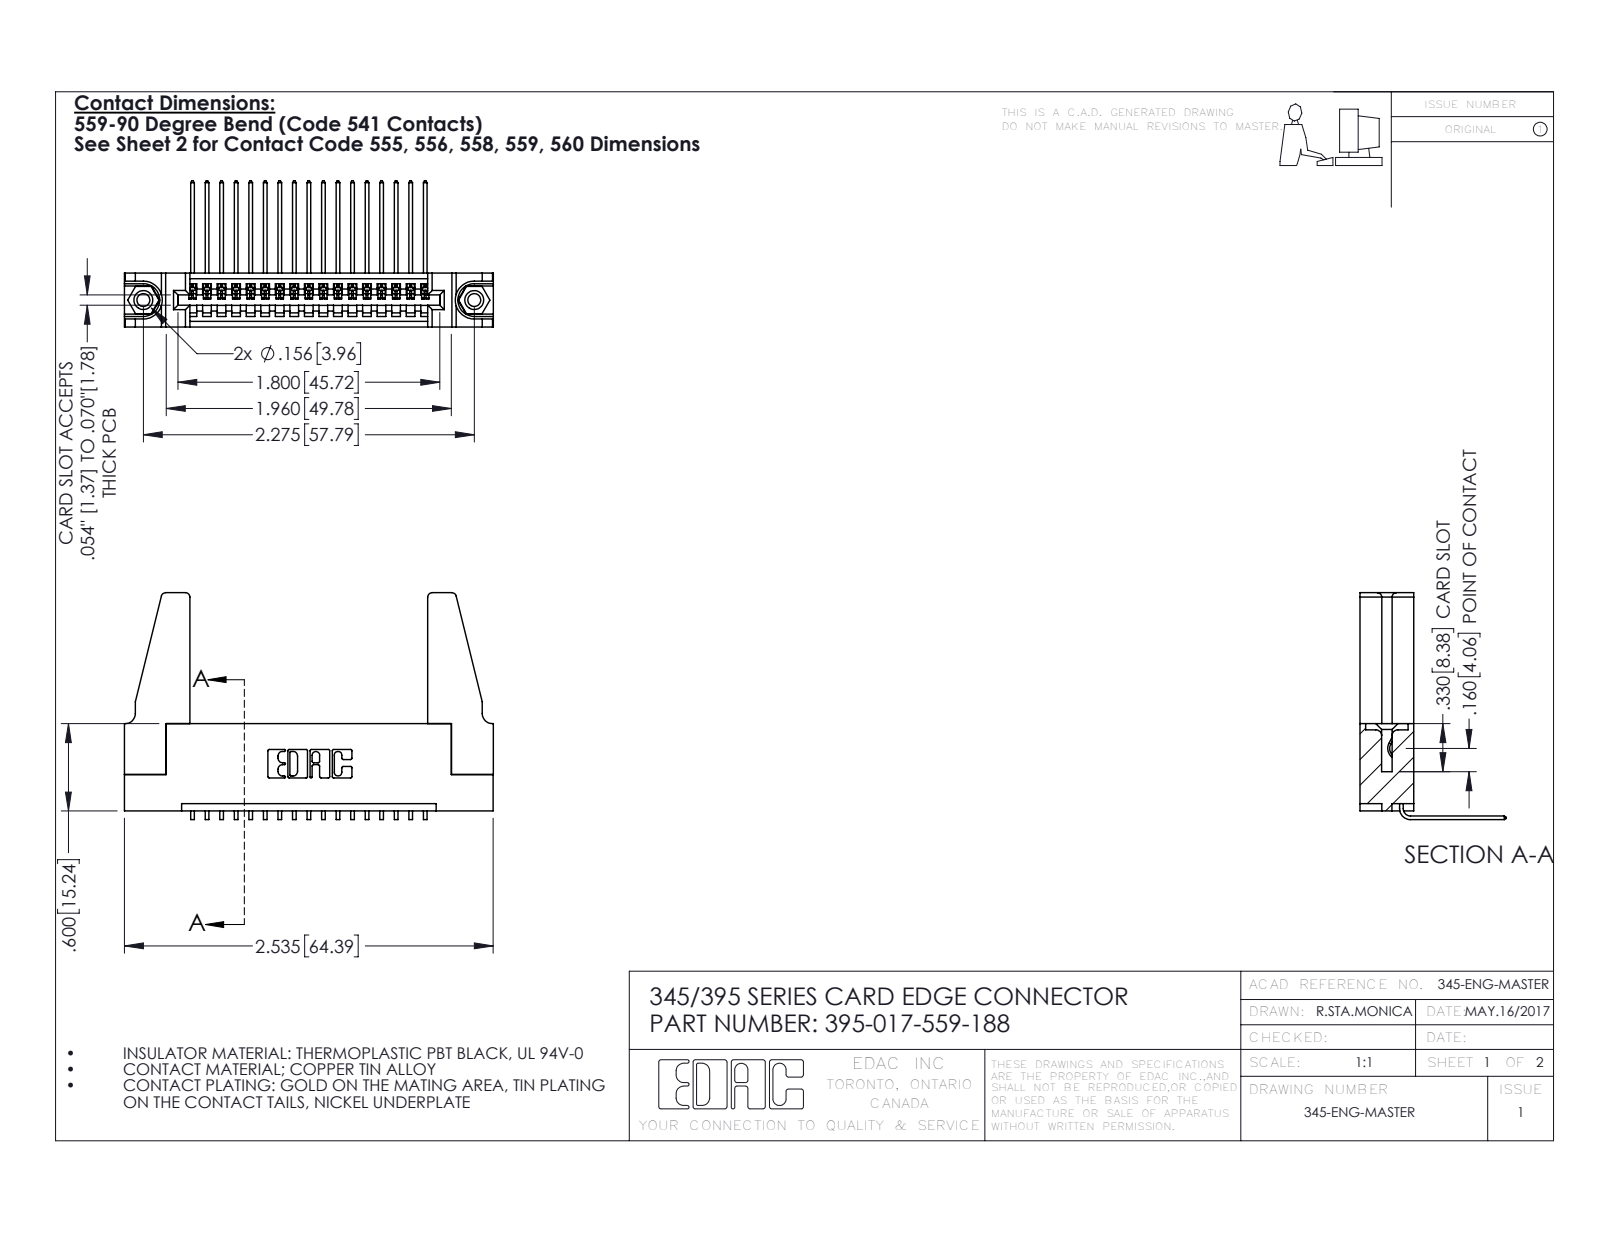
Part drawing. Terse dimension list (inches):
name: 345 Part_Flush Mounting Lugs - 0.156 Dia-TH; 345-292-001_558 559 Tail - 1; 345-220-078_345-220-088; 345-250-001_345-250-001-102 (+1 more)
written by: SolidWorks 2016 (CONFIG_CONTROL_DESIGN)
unit: in
bodies: 22 solids, 1270 faces (866 planar, 388 cylindrical, 16 other)
size: 2.536 × 1.559 × 1.005
volume: 0.563 in³; area: 17.14 in²
holes: 2× ⌀0.089, 2× ⌀0.125, 2× ⌀0.156, 1× ⌀0.064
bosses: 2× ⌀0.155
rounds: 34× R0.006, 22× R0.01, 8× R0.03, 6× R0.007, 6× R0.031, 3× R0.026, 2× R0.031, 2× R0.04
face distances: 0.37, 0.072, 0.298, 0.2, 0.098, 0.272, 0.025, 0.225, 0.15, 0.148
hole spacings: 0.27, 2.041, 2.275
